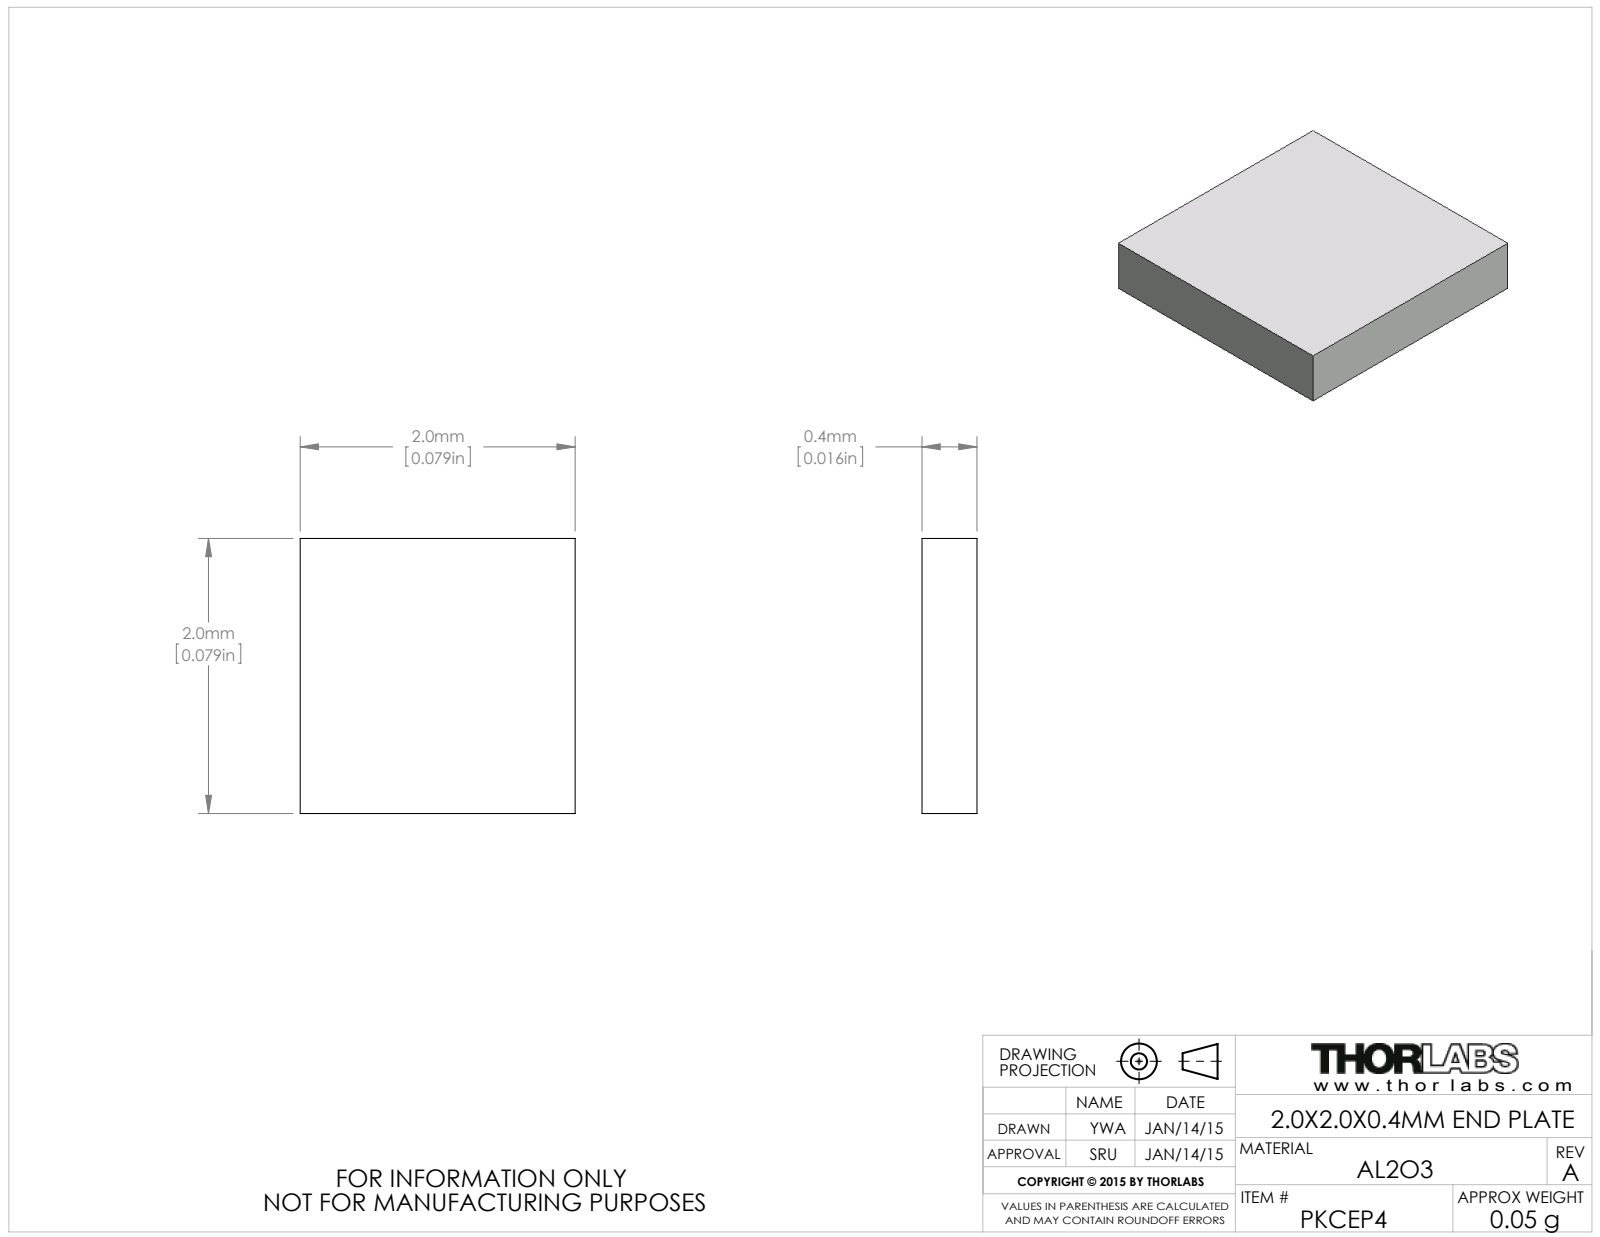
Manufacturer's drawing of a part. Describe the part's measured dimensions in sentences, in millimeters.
The part is named "PKCEP4". Its 3-D file was written by "SolidWorks 2012 (AUTOMOTIVE_DESIGN)". It is 1 solid with 6 faces: 6 planar, 0 cylindrical and 0 other. Overall it measures 2 by 2 by 0.4 millimeters. Its volume is 2 cubic millimeters and its surface area 11 square millimeters. The main face-to-face distances are 0.4, 2.
